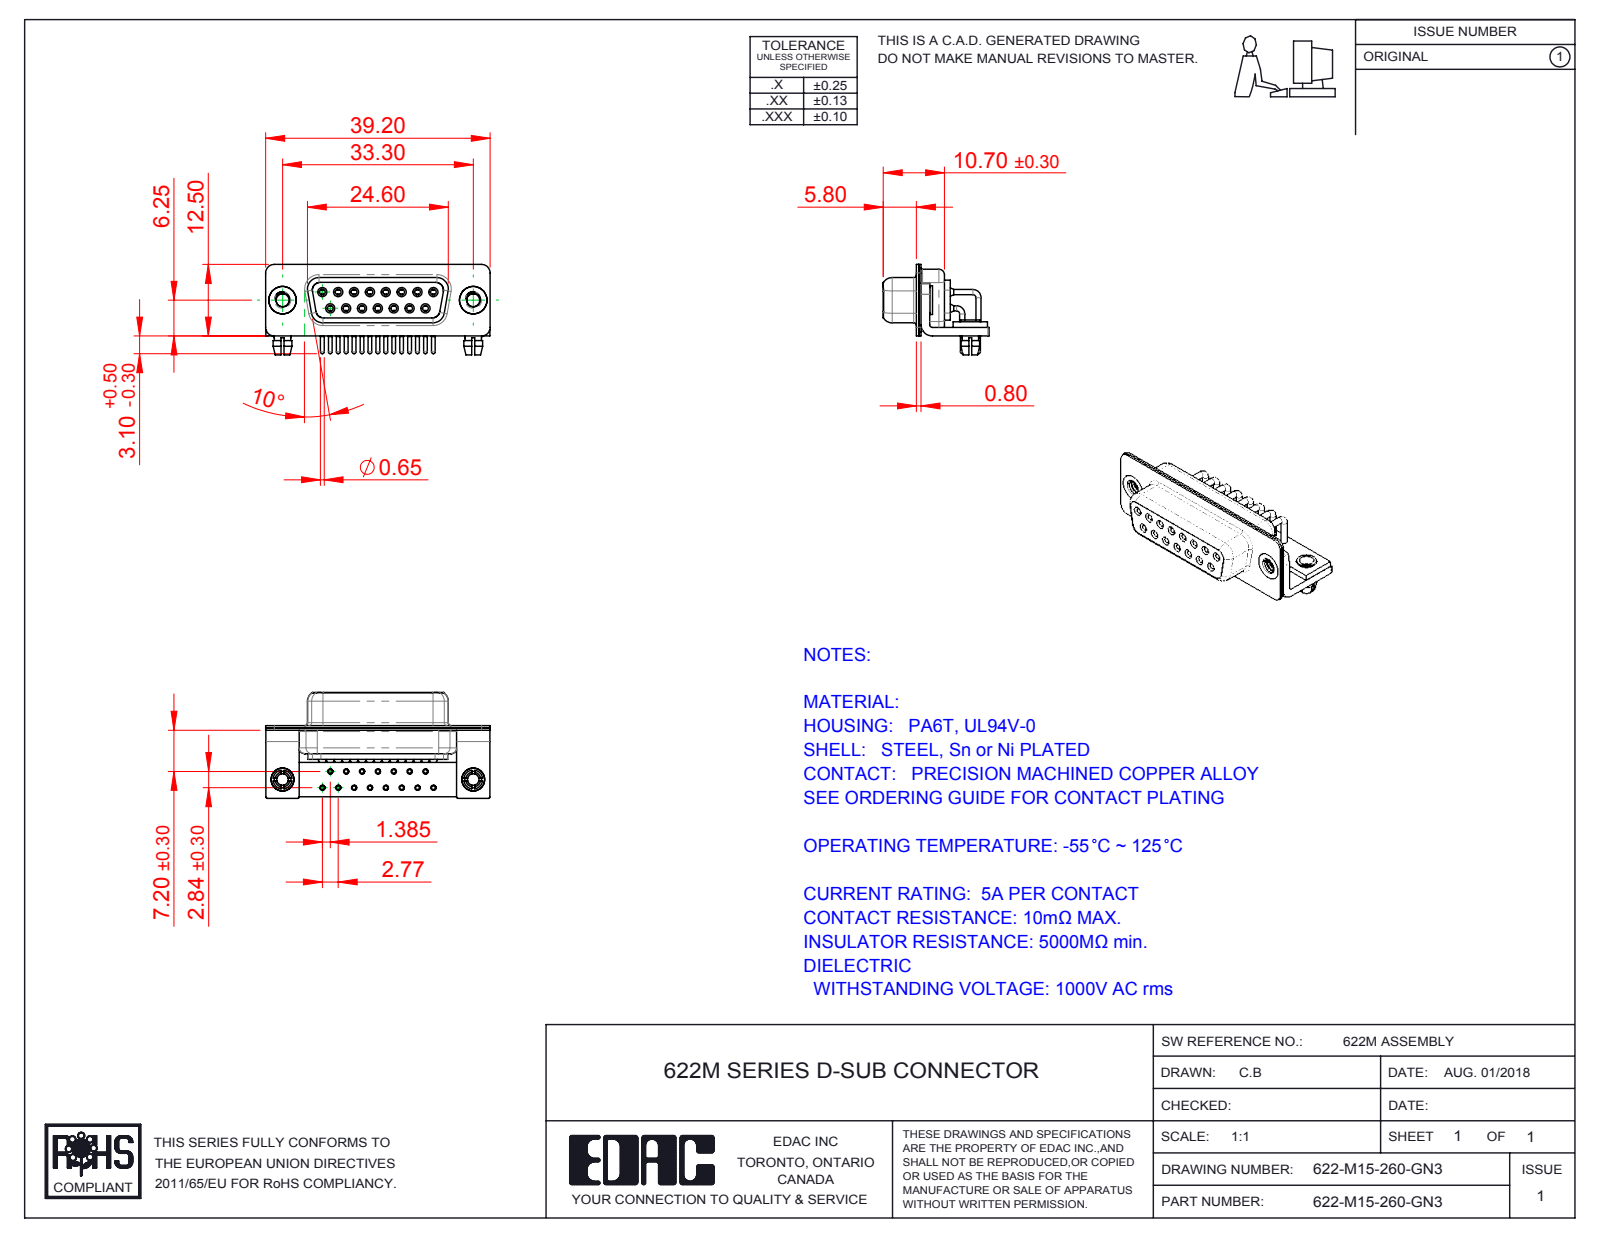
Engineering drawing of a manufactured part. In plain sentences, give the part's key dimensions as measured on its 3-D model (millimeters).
The part is named "622-M15-260-GN3; 622M Board Lock; 622M Stabilizer Board_15 Contacts; 622M Stabilizer Bracket (+6 more)". Its 3-D file was written by "SolidWorks 2016 (CONFIG_CONTROL_DESIGN)". It is 25 solids with 1246 faces: 366 planar, 566 cylindrical and 314 other. Overall it measures 39.2 by 18.5 by 15.8 millimeters. Its volume is 3 019 cubic millimeters and its surface area 7 749 square millimeters. Round holes: 17 of diameter 2, 15 of diameter 0.9, 15 of diameter 1, 15 of diameter 1.1, 15 of diameter 1.7, 15 of diameter 1.8, 2 of diameter 2.26, 2 of diameter 2.5, 2 of diameter 3.2, 2 of diameter 4, 2 of diameter 4.8. Round bosses or shafts: 22 of diameter 0.9, 15 of diameter 1.6, 15 of diameter 1.5, 15 of diameter 0.65, 2 of diameter 5, 2 of diameter 4.9, 2 of diameter 4, 2 of diameter 3.4. Partial cylindrical surfaces (rounded edges, fillets, slot ends): 16 of radius 0.25, 16 of radius 1.5, 13 of radius 2, 8 of radius 1.35, 8 of radius 1.6, 5 of radius 0.5, 4 of radius 0.6, 4 of radius 0.65. The main face-to-face distances are 0.4, 0.8, 2.3, 1.9, 9.35, 1.5, 1, 1.45, 8.95, 0.85. The hole center spacings are 3.16, 2.77, 5.54, 8.31, 11.08, 5.03, 5.04, 7.48.
